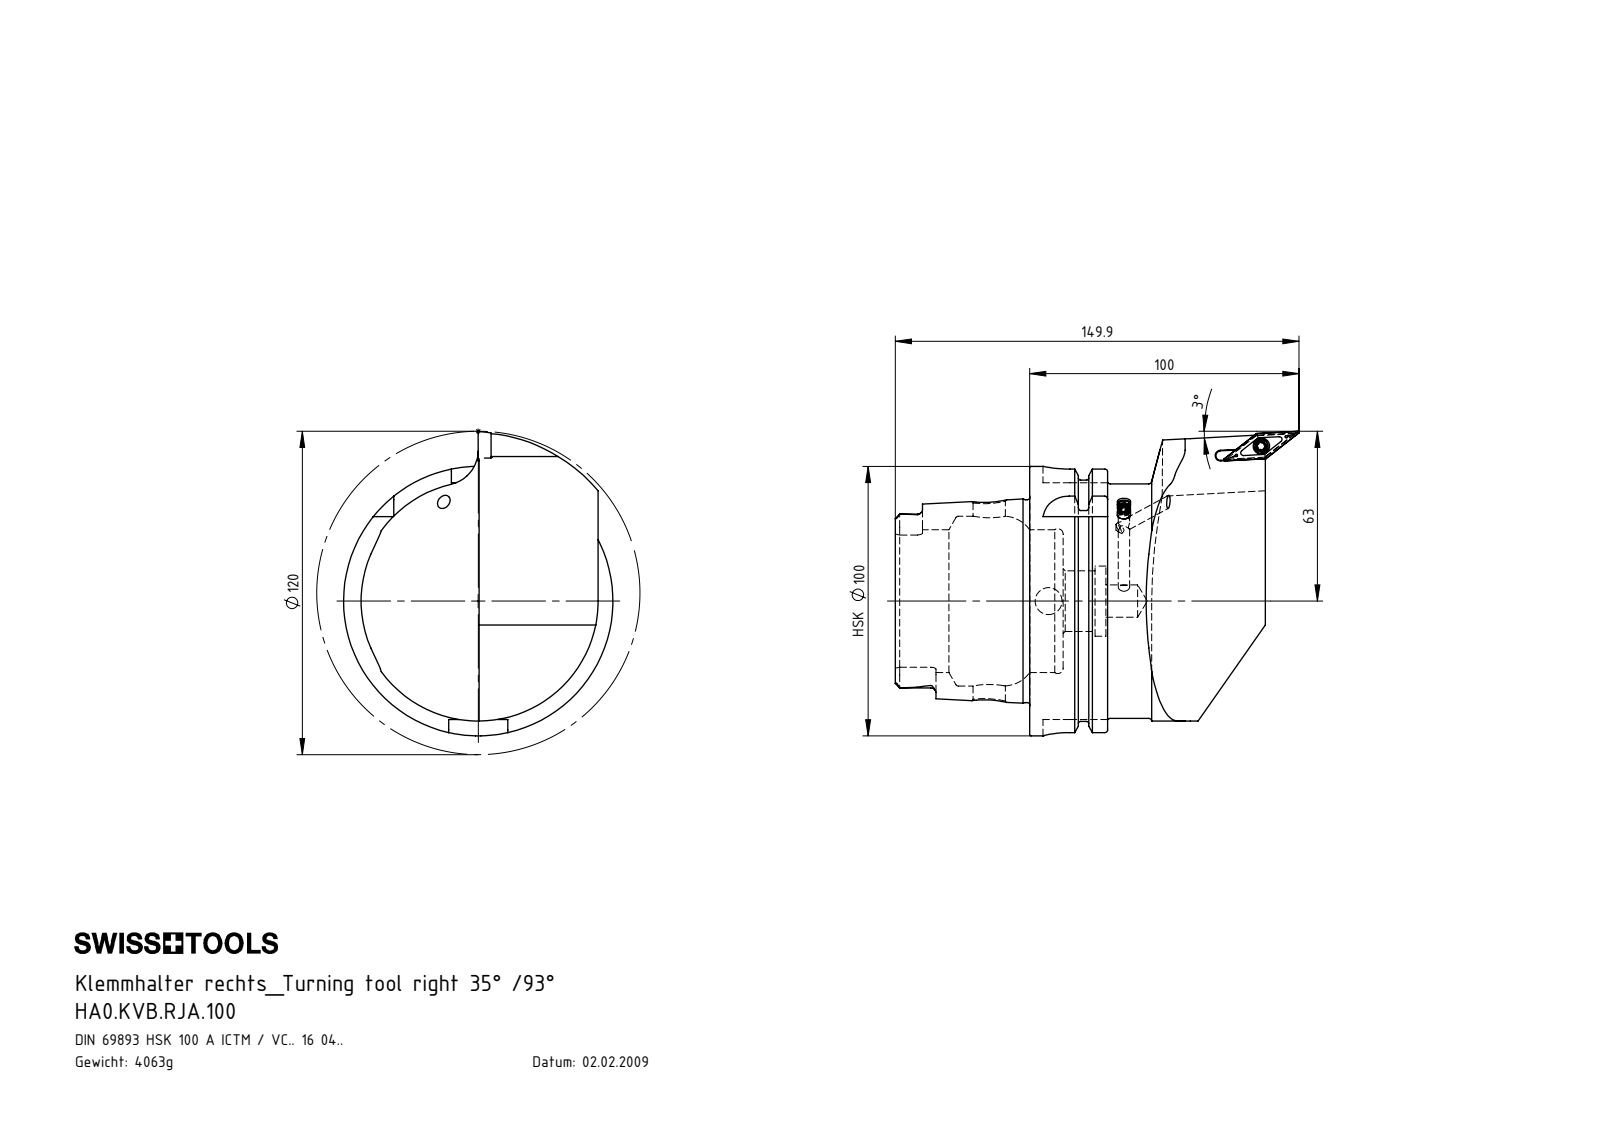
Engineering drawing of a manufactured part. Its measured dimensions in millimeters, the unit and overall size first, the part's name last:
Units: millimetres
Overall size (bounding box): 149.93 × 113 × 100
Round holes (diameter × count): ⌀4.2 ×2, ⌀12 ×2, ⌀3.3 ×1, ⌀4 ×1, ⌀4.4 ×1, ⌀6.1 ×1, ⌀10 ×1, ⌀22.5 ×1, ⌀26 ×1, ⌀53 ×1, ⌀63 ×1
Round bosses / shafts (diameter × count): ⌀100 ×1, ⌀91.95 ×1, ⌀87 ×1, ⌀75.26 ×1, ⌀5.25 ×1, ⌀5 ×1, ⌀4 ×1
Partial cylindrical surfaces — rounded edges, fillets, slot ends (radius × count): R0.34 ×6, R0.59 ×6, R1.9 ×6, R10 ×4, R4.83 ×2, R4.88 ×2, R1.75 ×1, R6 ×1
Main face-to-face distances: 87.5, 44.2, 12.45, 75.05, 28.95, 16.5, 58.55, 49.9, 62.35, 78.85
Hole centre spacings: 97.62, 97.73
Volume: 517 130 mm³ · Surface area: 67 934 mm²
Bodies: 5 solids, 309 faces (77 planar, 91 cylindrical, 141 other)
Part name (STEP PRODUCT): HA0.KVB.RJA.100; KVT_MB_600_050; WCB-ER2.001.009_A; VCMT160404 (+1 more)
STEP written by: SolidWorks 2012 (AUTOMOTIVE_DESIGN)
